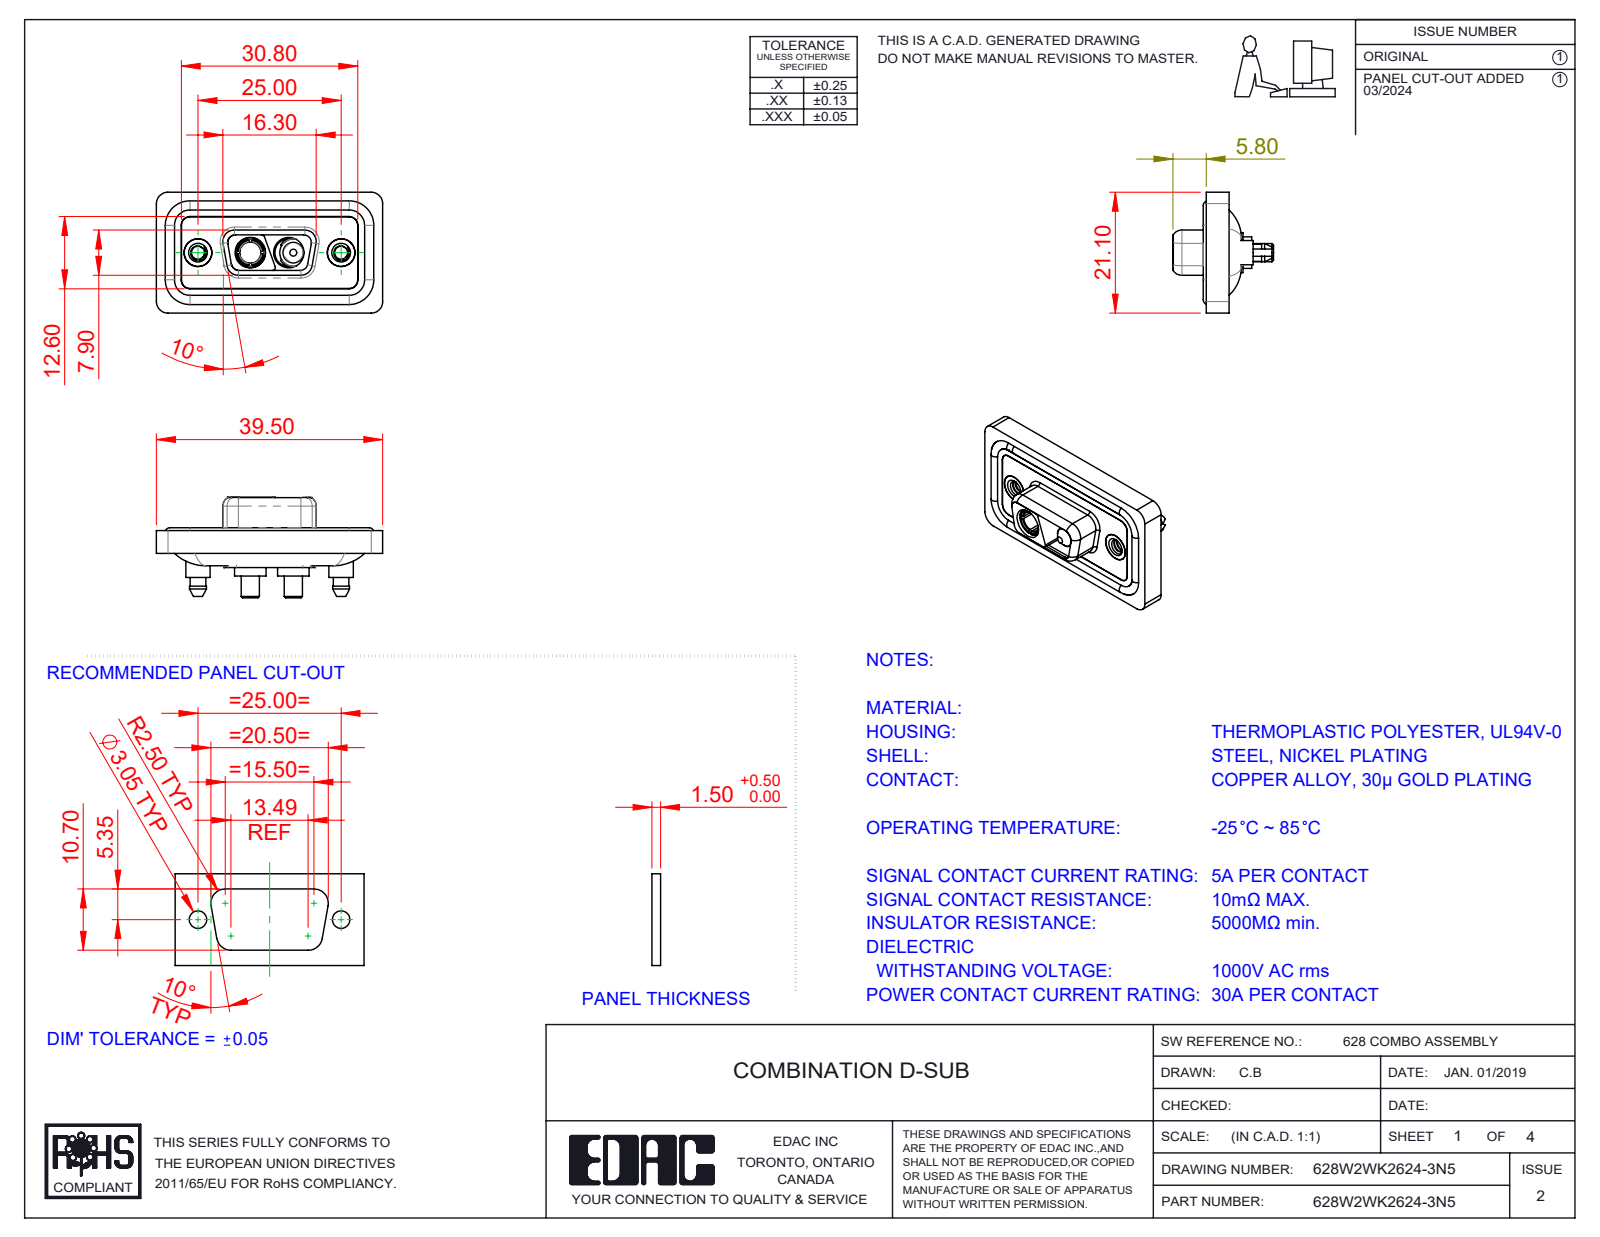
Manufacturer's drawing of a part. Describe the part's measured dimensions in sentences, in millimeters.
The part is named "628Combo Threaded Boardlock_5; Power Pin_30A S; 628Combo Housing_2WK2; 628Combo Waterproof Housing_09 Contacts (+4 more)". Its 3-D file was written by "SolidWorks 2023 (CONFIG_CONTROL_DESIGN)". It is 11 solids with 550 faces: 160 planar, 263 cylindrical and 127 other. Overall it measures 39.5 by 21.1 by 17.55 millimeters. Its volume is 4 751 cubic millimeters and its surface area 7 686 square millimeters. Round holes: 4 of diameter 4.85, 2 of diameter 2.26, 2 of diameter 4, 2 of diameter 4.05, 2 of diameter 5, 2 of diameter 5.3, 1 of diameter 3.7. Round bosses or shafts: 4 of diameter 1.6, 2 of diameter 5.5, 2 of diameter 5.4, 2 of diameter 5.2, 2 of diameter 4.95, 2 of diameter 4.8, 2 of diameter 4.75, 2 of diameter 4.25. Partial cylindrical surfaces (rounded edges, fillets, slot ends): 24 of radius 1.5, 18 of radius 2, 10 of radius 1.6, 8 of radius 1.35, 6 of radius 0.5, 4 of radius 0.25, 4 of radius 0.6, 4 of radius 0.65. The main face-to-face distances are 0.4, 1.1, 2.9, 1.6, 0.5, 1.8, 5.65, 1.5, 4, 5.35. The hole center spacings are 9.14, 15.86, 6.72, 25.
